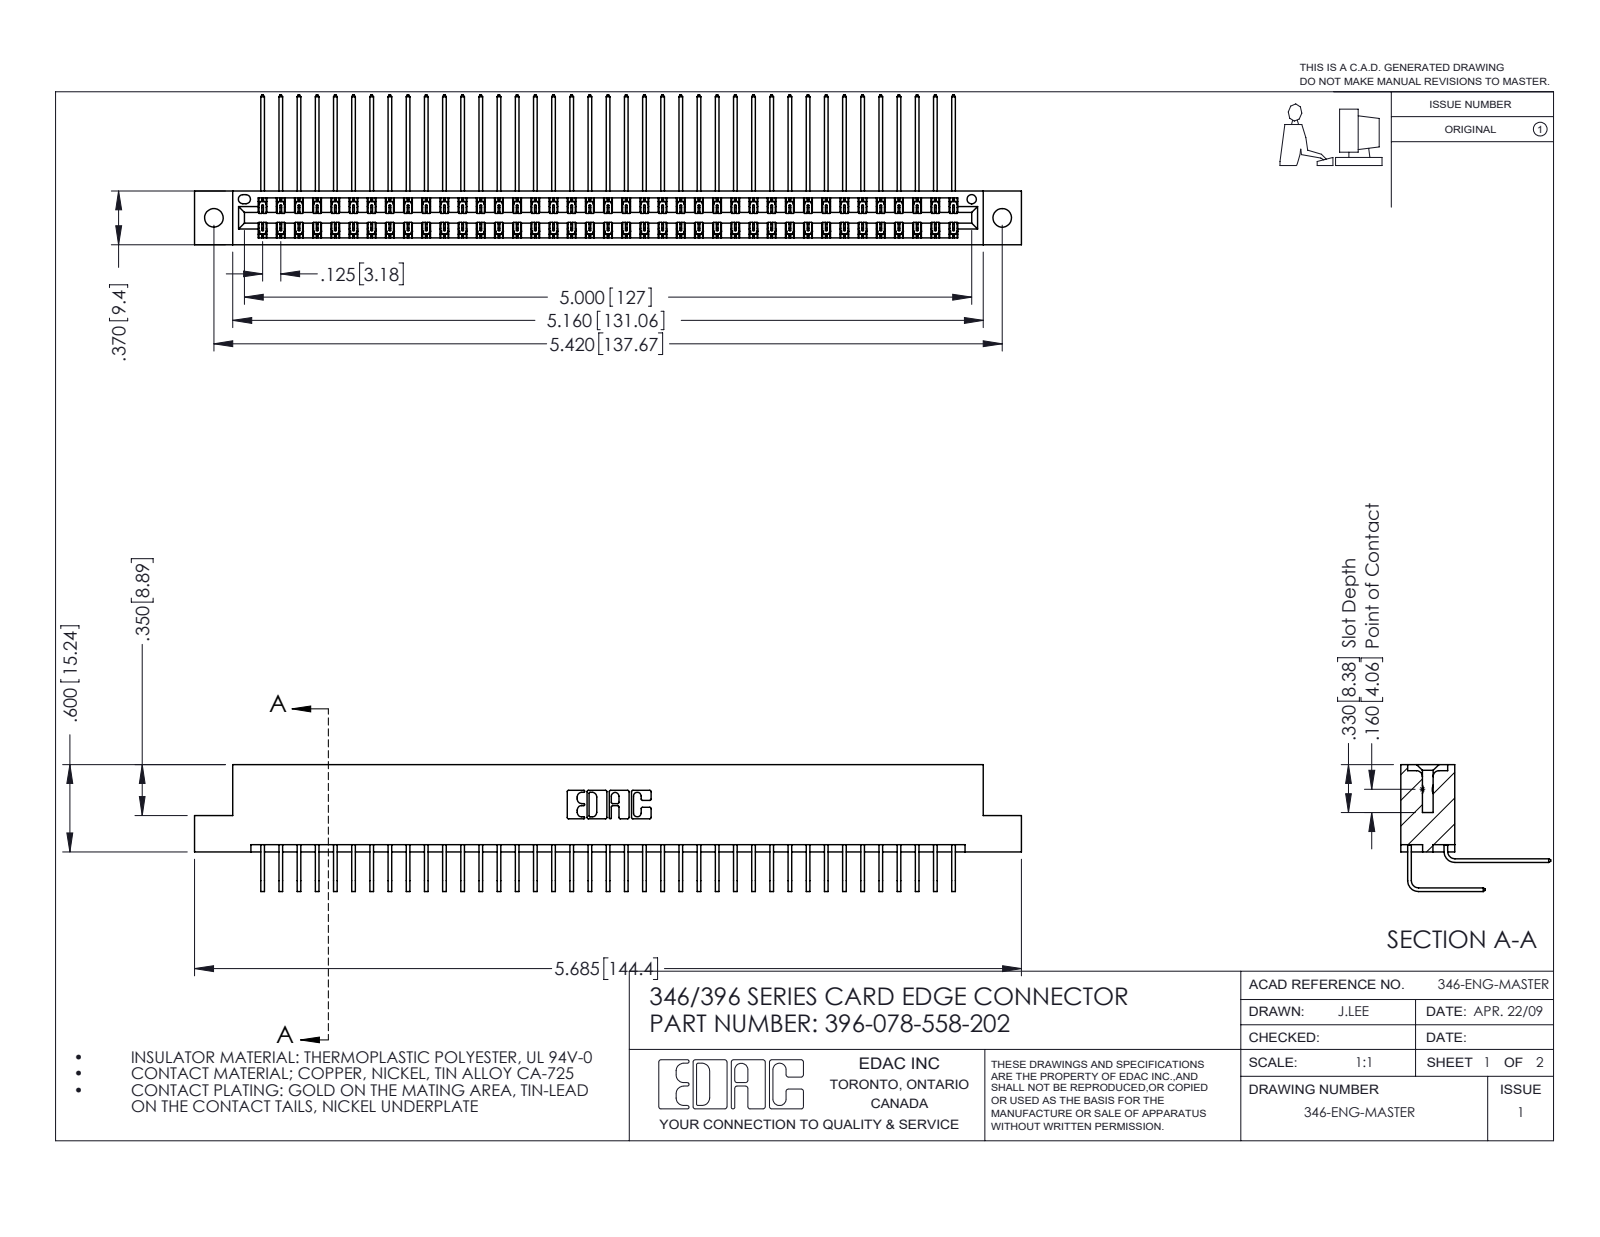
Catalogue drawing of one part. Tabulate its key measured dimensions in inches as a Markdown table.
| quantity | value |
| --- | --- |
| part name | 346 Part_Flush Mounting Lugs - 0.128 Dia; 345-292-001_558 Tail - 2; 396-078-558-202; 345-292-001_558 559 Tail - 1 |
| STEP written by | SolidWorks 2016 (CONFIG_CONTROL_DESIGN) |
| units | inches |
| bodies | 79 solids, 4334 faces (2962 planar, 1372 cylindrical, 0 other) |
| overall size | 5.685 × 1.03 × 0.873 |
| volume | 0.883 in³ |
| surface area | 33.69 in² |
| round holes (diameter × count) | 0.128 × 2, 0.064 × 1 |
| partial cylindrical surfaces (radius × count) | 0.006 × 117, 0.01 × 22, 0.007 × 6, 0.031 × 6, 0.026 × 3, 0.014 × 2, 0.022 × 2, 0.024 × 2 |
| main face-to-face distances | 0.048, 0.322, 0.025, 0.37, 0.25, 0.072, 0.298, 0.275, 0.148, 0.222 |
| hole center spacings | 0.246, 5.211, 5.42 |
